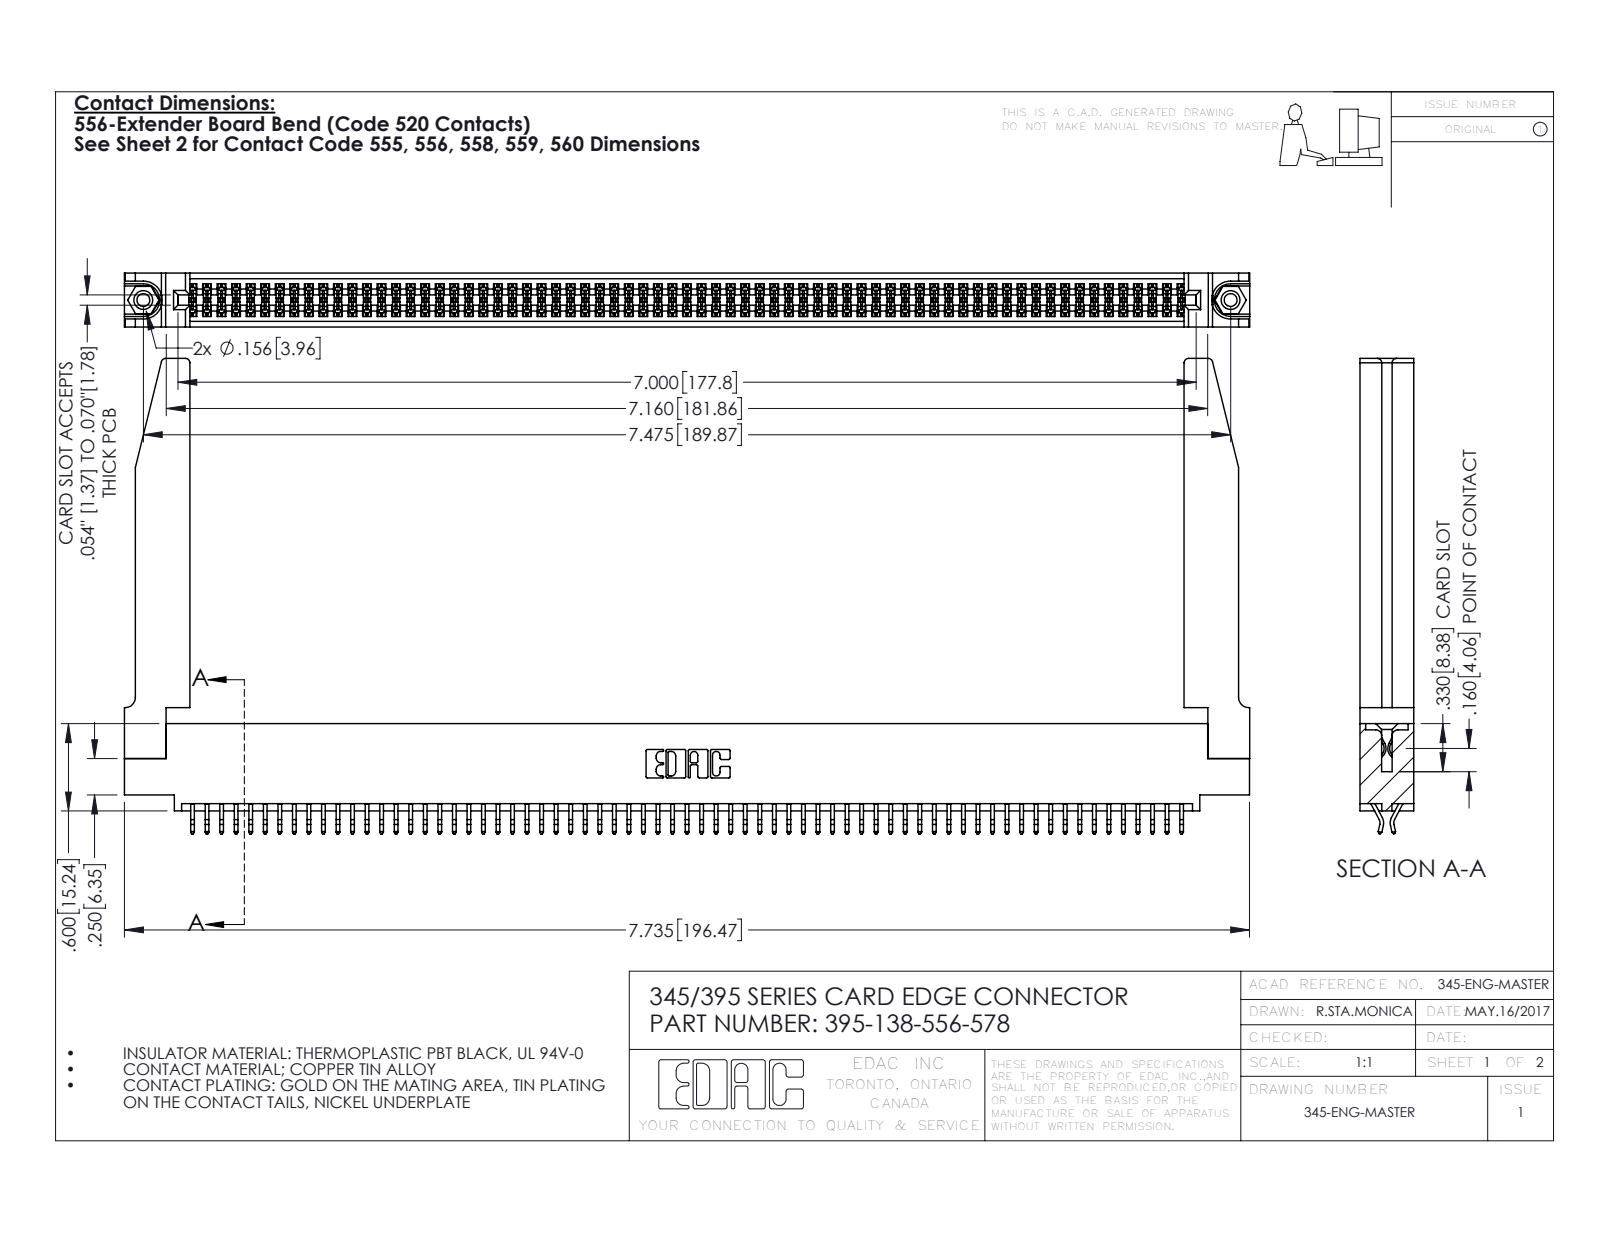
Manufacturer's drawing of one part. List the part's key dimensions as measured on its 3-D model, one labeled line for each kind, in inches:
Part name (STEP PRODUCT): 345-292-001_556 Tail; 345-220-078_345-220-078; 395-138-556-578; 345-250-001_345-250-001-102 (+1 more)
STEP written by: SolidWorks 2016 (CONFIG_CONTROL_DESIGN)
Units: inches
Bodies: 143 solids, 8092 faces (5332 planar, 2708 cylindrical, 52 other)
Overall size (bounding box): 7.736 × 3.267 × 0.37
Volume: 1.649 in³ · Surface area: 55.49 in²
Round holes (diameter × count): ⌀0.089 ×2, ⌀0.125 ×2, ⌀0.156 ×2, ⌀0.064 ×1
Round bosses / shafts (diameter × count): ⌀0.155 ×2
Partial cylindrical surfaces — rounded edges, fillets, slot ends (radius × count): R0.006 ×207, R0.01 ×22, R0.03 ×8, R0.007 ×6, R0.031 ×6, R0.026 ×3, R0.01 ×2, R0.014 ×2
Main face-to-face distances: 0.072, 0.298, 0.37, 0.025, 0.098, 0.272, 0.2, 0.225, 0.175, 0.149
Hole centre spacings: 0.27, 7.239, 7.475
